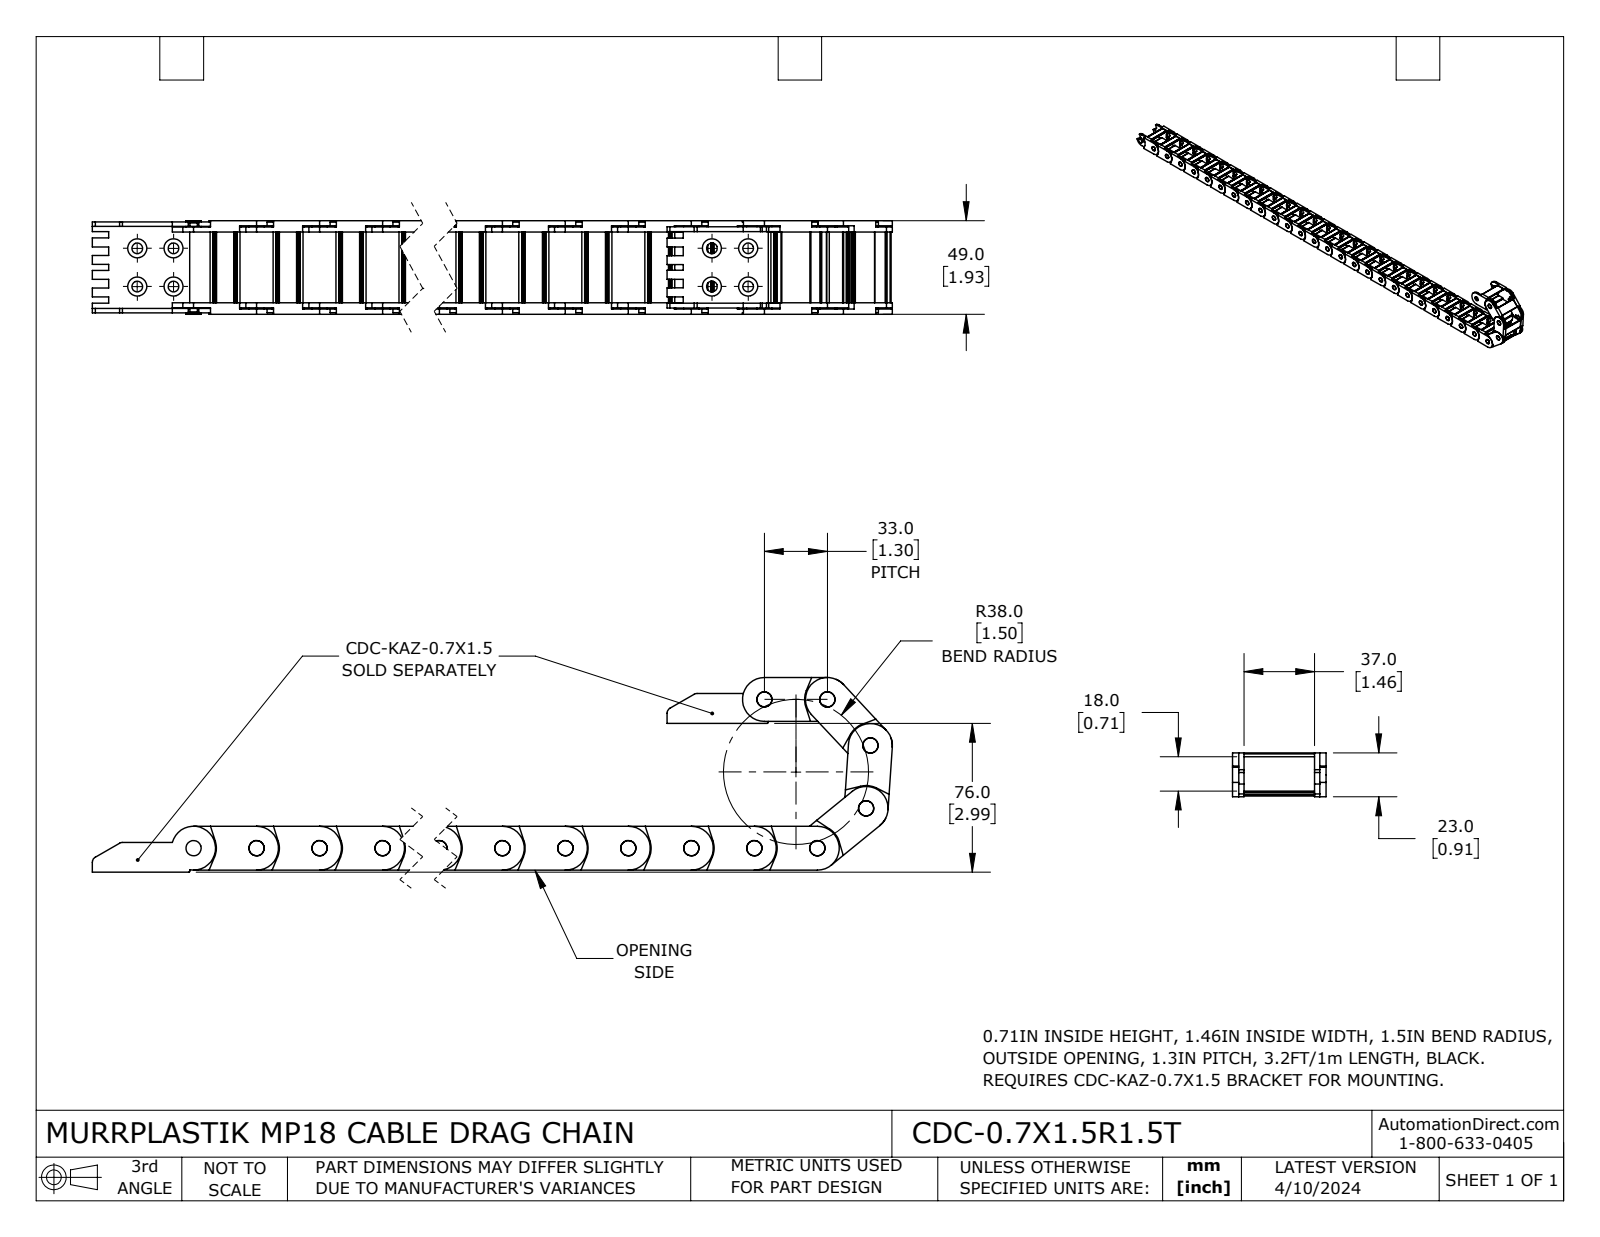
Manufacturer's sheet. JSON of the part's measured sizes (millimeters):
{"part_name": "CDC-0.7X1.5R1.5T", "step_written_by": "SolidWorks 2023 (CONFIG_CONTROL_DESIGN)", "units": "millimeters", "bodies": {"solids": 30, "faces": 2280, "planar": 1110, "cylindrical": 1170, "other": 0}, "overall_size": [908.49, 100.88, 49], "volume_mm3": 289410, "surface_area_mm2": 238745, "round_holes": [[8, 30]], "round_bosses_or_shafts": [[8, 1]], "partial_cylinders_radius": [[0.5, 120], [1.5, 120], [0.2, 60], [0.3, 60], [11.5, 31], [11.95, 31], [5, 30], [5.45, 30]], "face_to_face_distances": [43, 2.7, 3.3, 6, 49, 45.7, 39.7, 46.3, 0.6, 40.3], "hole_center_spacings": [33, 66, 99, 132, 165, 198, 231, 264]}
